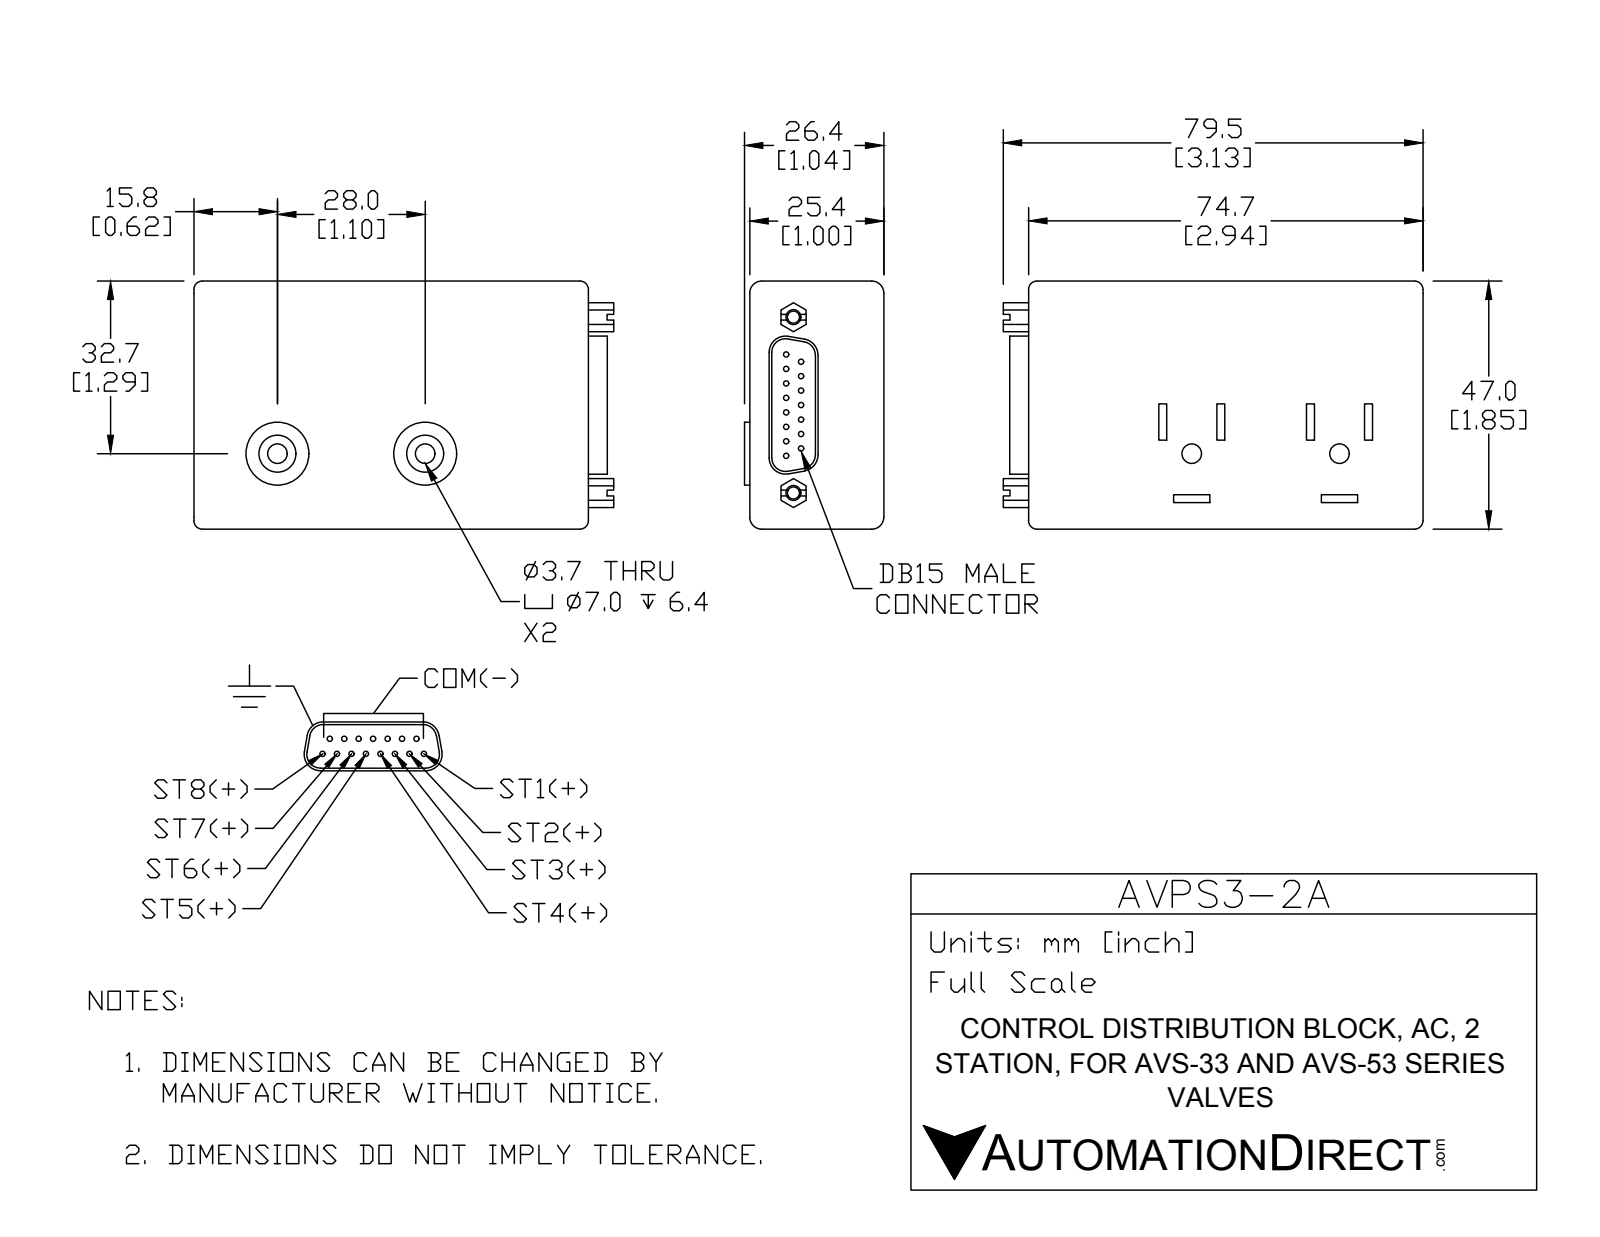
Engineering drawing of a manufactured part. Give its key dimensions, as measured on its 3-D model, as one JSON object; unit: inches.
{"part_name": "AVPS3-2A", "step_written_by": "SolidWorks 2016 (AUTOMOTIVE_DESIGN)", "units": "inches", "bodies": {"solids": 1, "faces": 173, "planar": 93, "cylindrical": 68, "other": 12}, "overall_size": [3.131, 1.85, 1.04], "volume_in3": 5.33, "surface_area_in2": 23.64, "round_holes": [[0.089, 2], [0.145, 2], [0.275, 2]], "round_bosses_or_shafts": [[0.039, 15], [0.469, 2]], "partial_cylinders_radius": [[0.062, 6], [0.09, 4], [0.102, 4], [0.122, 4], [0.063, 2]], "face_to_face_distances": [1, 1.85, 2.942, 0.059, 1.102, 0.123, 2.819, 0.433, 0.02, 0.04], "hole_center_spacings": [1.102, 1.311]}
